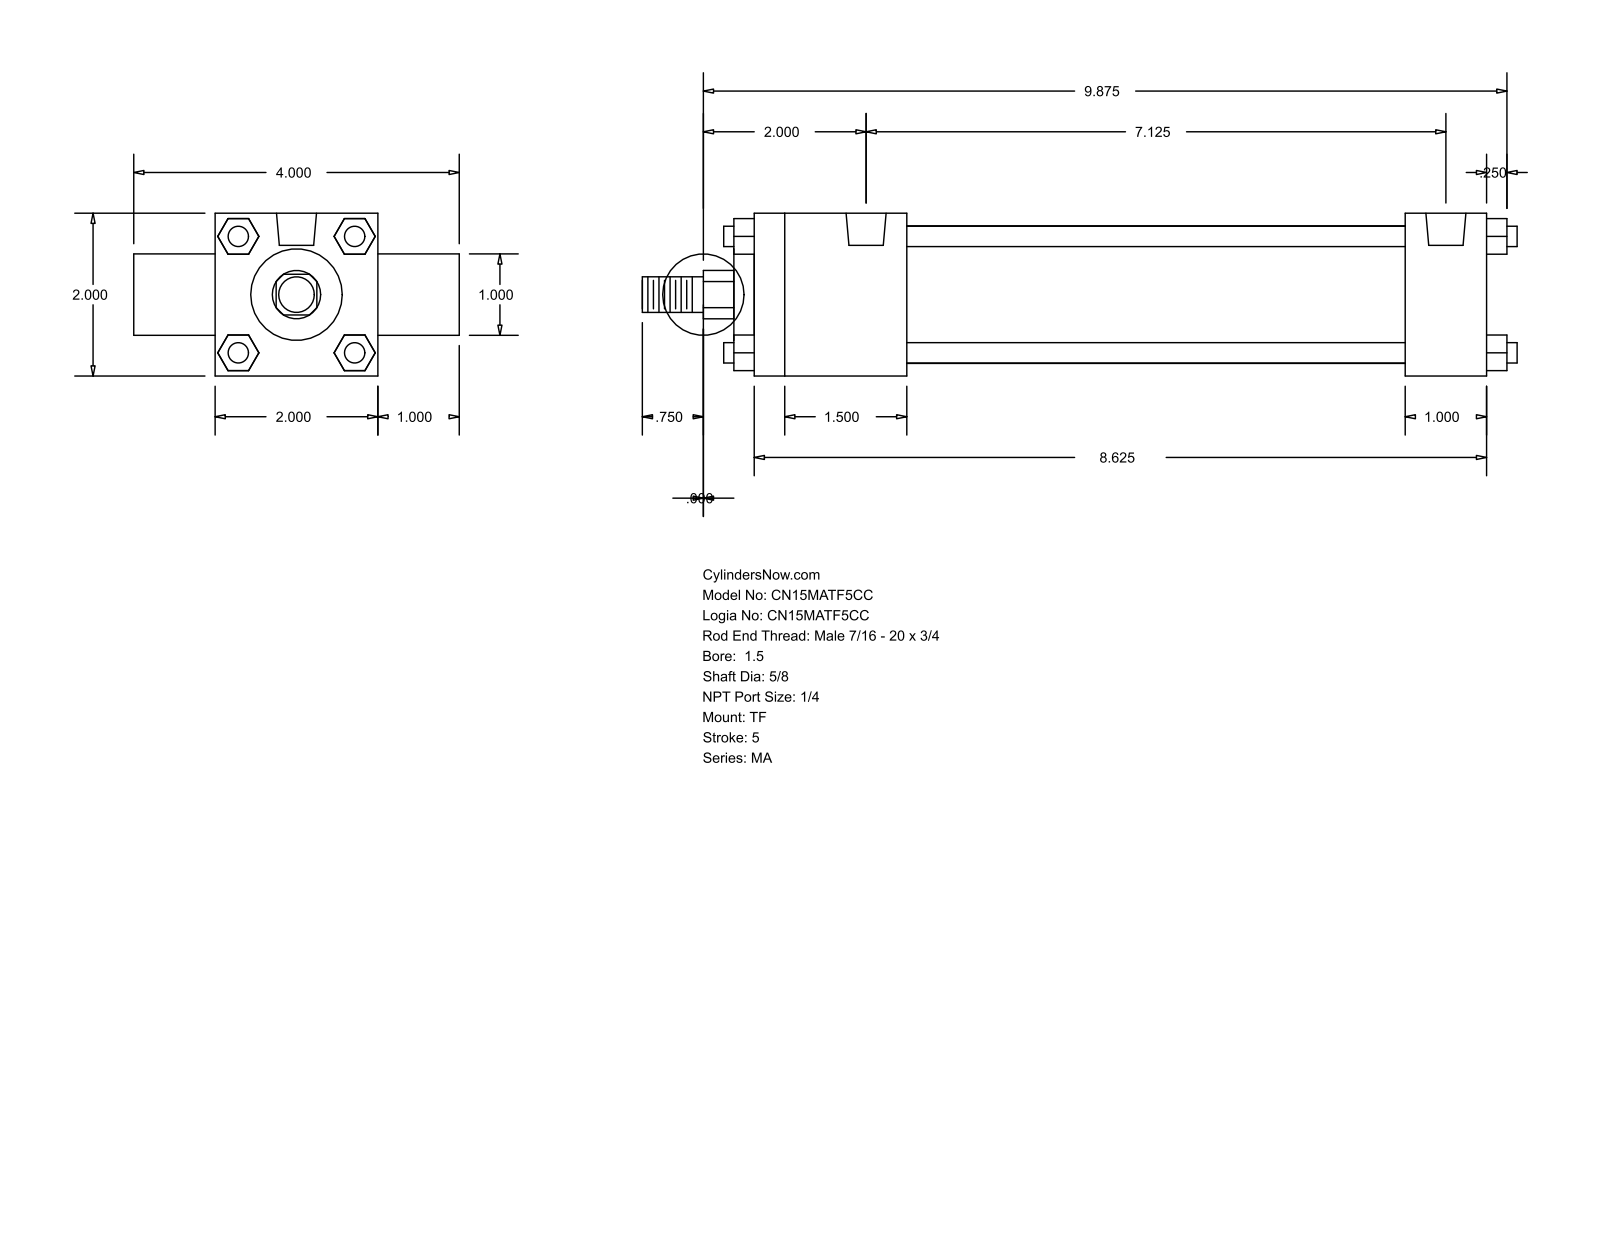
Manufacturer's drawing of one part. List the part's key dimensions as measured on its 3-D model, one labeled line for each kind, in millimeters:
Part name (STEP PRODUCT): MA_TF__0150_0.625
STEP written by: GSSL Pune (CONFIG_CONTROL_DESIGN)
Units: millimetres
Bodies: 0 solids, 120 faces (92 planar, 28 cylindrical, 0 other)
Overall size (bounding box): 273.05 × 101.6 × 50.8
Round holes (diameter × count): ⌀7.94 ×3, ⌀12.49 ×2
Round bosses / shafts (diameter × count): ⌀6.35 ×4, ⌀42.93 ×1, ⌀28.57 ×1, ⌀25.4 ×1, ⌀15.88 ×1, ⌀11.11 ×1
Partial cylindrical surfaces — rounded edges, fillets, slot ends (radius × count): R7.54 ×1
Main face-to-face distances: 50.8, 25.4, 228.59, 6.35, 234.94, 76.2, 47.62, 203.19, 155.57, 180.97
Hole centre spacings: 180.98
